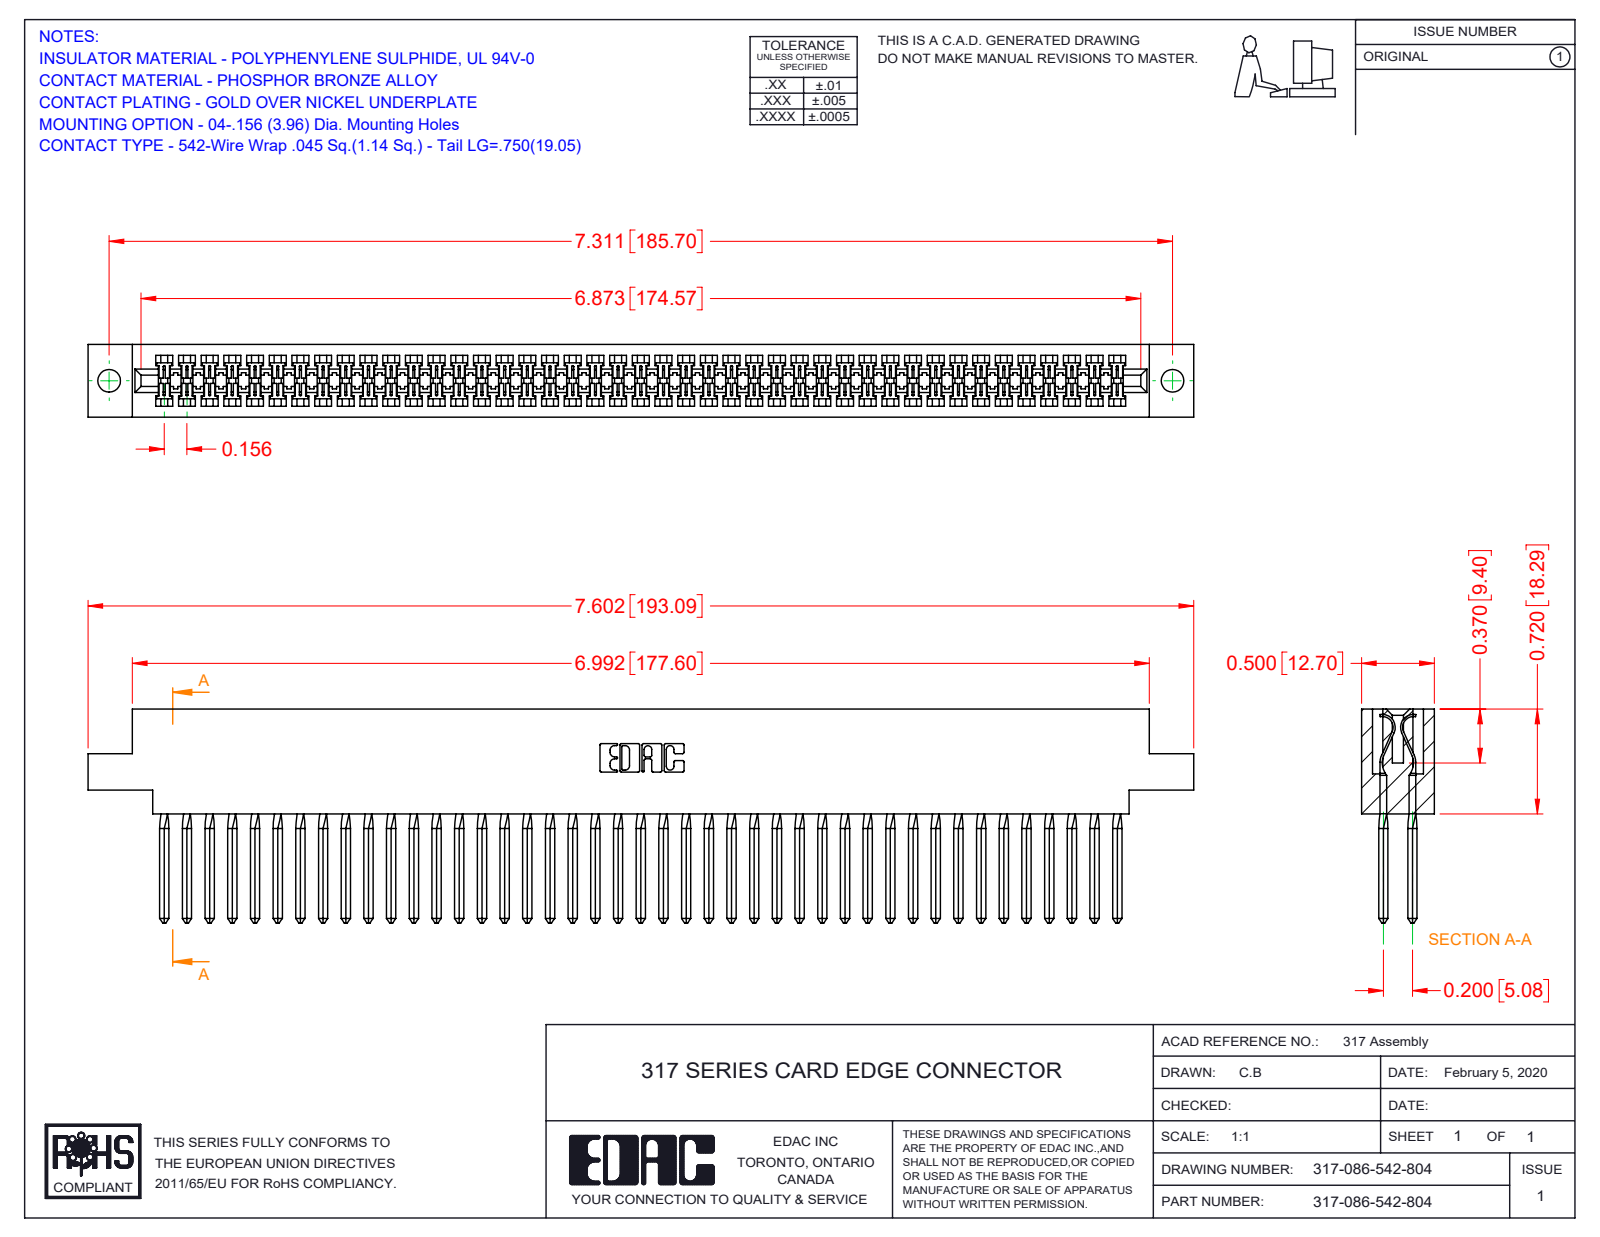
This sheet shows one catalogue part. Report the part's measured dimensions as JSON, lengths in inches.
{"part_name": "317 Part_.156 Dia - TH; 317-086-542-804; 317-290-003_542", "step_written_by": "SolidWorks 2016 (CONFIG_CONTROL_DESIGN)", "units": "inches", "bodies": {"solids": 87, "faces": 5004, "planar": 4014, "cylindrical": 646, "other": 344}, "overall_size": [7.602, 1.47, 0.5], "volume_in3": 1.926, "surface_area_in2": 67.8, "round_holes": [[0.156, 2]], "partial_cylinders_radius": [[0.006, 172], [0.01, 22], [0.007, 6], [0.031, 6], [0.026, 3], [0.074, 2], [0.089, 2], [0.1, 2]], "face_to_face_distances": [0.5, 0.075, 0.425, 0.35, 0.2, 0.046, 0.128, 0.372, 0.052, 0.297], "hole_center_spacings": [7.311]}
